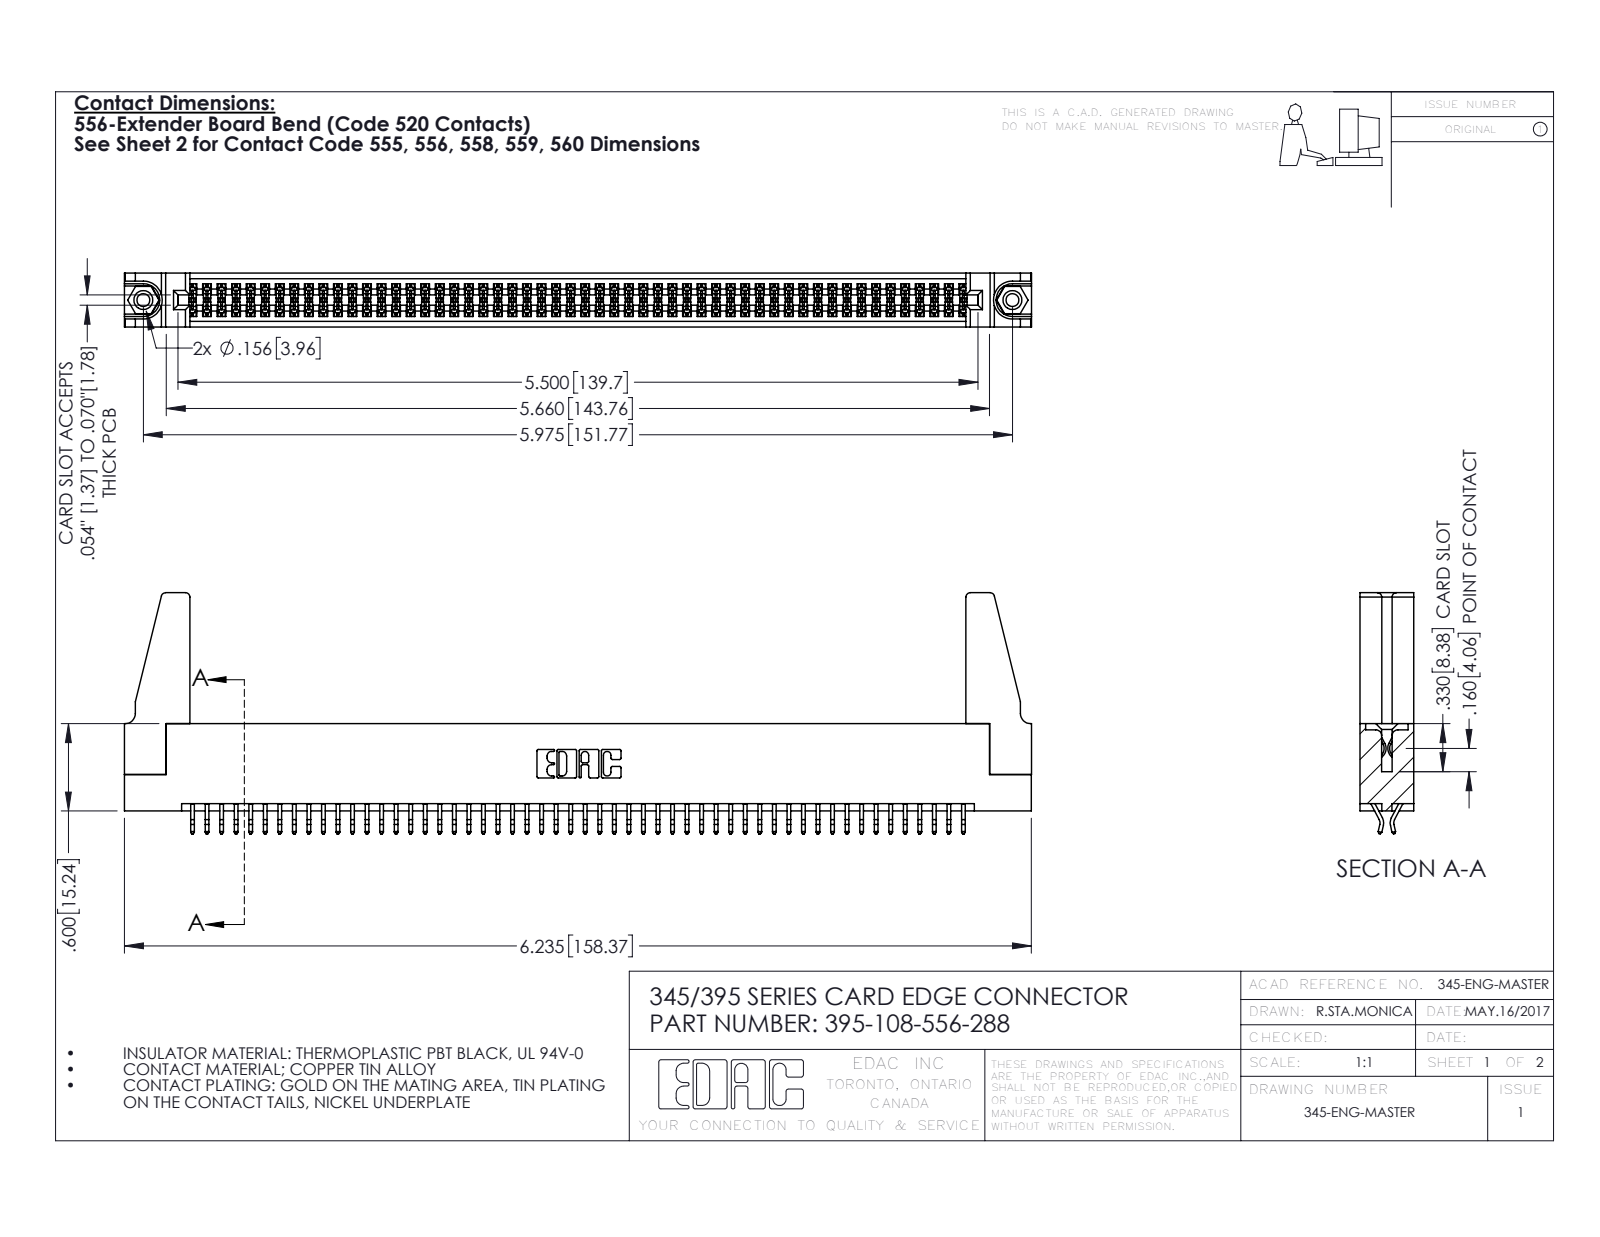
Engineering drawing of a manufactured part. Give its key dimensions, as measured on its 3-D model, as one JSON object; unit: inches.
{"part_name": "345 Part_Flush Mounting Lugs - 0.156 Dia-TH; 345-292-001_556 Tail; 395-108-556-288; 345-250-001_345-250-001-102 (+1 more)", "step_written_by": "SolidWorks 2016 (CONFIG_CONTROL_DESIGN)", "units": "inches", "bodies": {"solids": 113, "faces": 6298, "planar": 4148, "cylindrical": 2134, "other": 16}, "overall_size": [6.236, 1.657, 0.37], "volume_in3": 1.144, "surface_area_in2": 40.55, "round_holes": [[0.089, 2], [0.125, 2], [0.156, 2], [0.064, 1]], "round_bosses_or_shafts": [[0.155, 2]], "partial_cylinders_radius": [[0.006, 162], [0.01, 22], [0.03, 8], [0.007, 6], [0.031, 6], [0.026, 3], [0.01, 2], [0.014, 2]], "face_to_face_distances": [0.072, 0.298, 0.37, 0.2, 0.025, 0.098, 0.272, 0.225, 0.175, 0.149], "hole_center_spacings": [0.27, 5.739, 5.975]}
